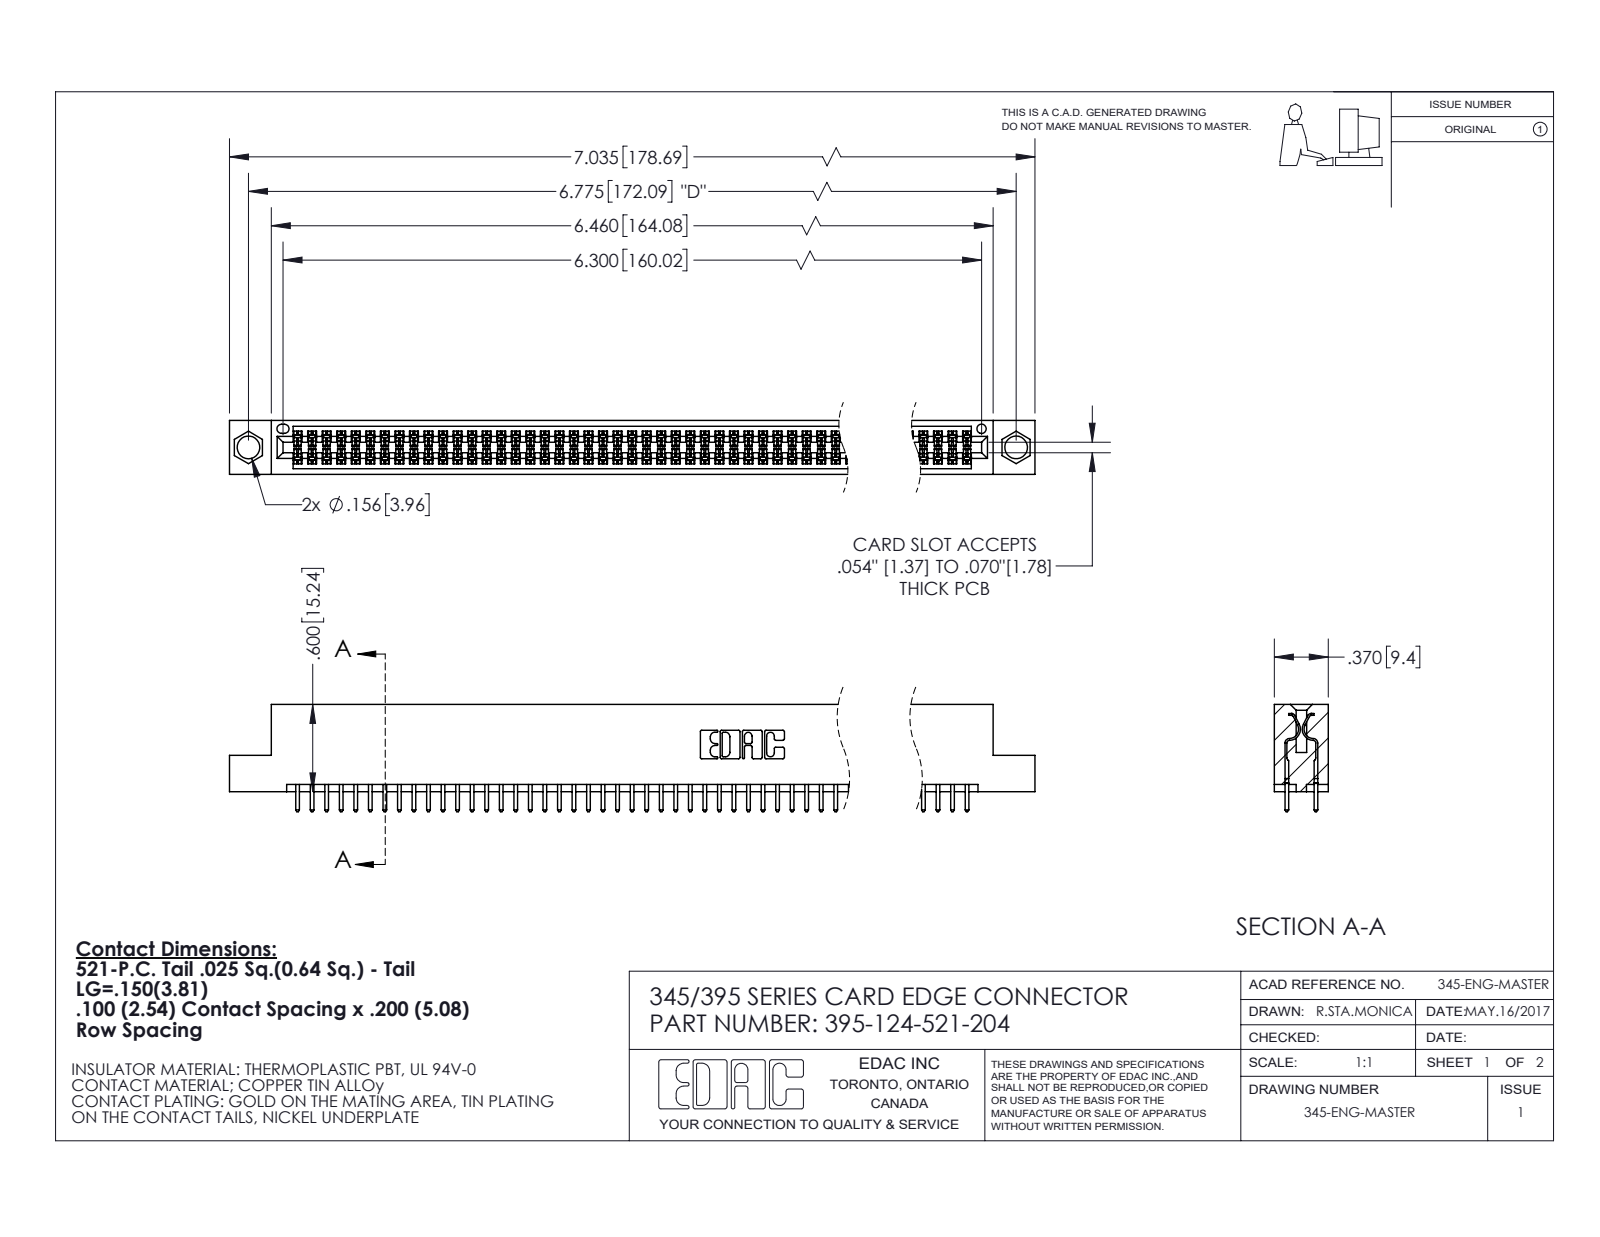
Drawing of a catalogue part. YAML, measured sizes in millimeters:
part_name: "345 Part_Flush Mounting Lugs - 0.156 Dia-TI; 395-124-521-204; 345-292-001_345-293-121"
step_written_by: "SolidWorks 2020 (CONFIG_CONTROL_DESIGN)"
units: millimeters
bodies: {solids: 125, faces: 6340, planar: 4186, cylindrical: 2154, other: 0}
overall_size: [178.7, 18.7, 9.4]
volume: 17390
surface_area: 25610
round_holes:
  - {diameter: 4, count: 2}
  - {diameter: 1.6, count: 1}
partial_cylinders:
  - {radius: 0.2, count: 247}
  - {radius: 0.3, count: 124}
  - {radius: 0.3, count: 22}
  - {radius: 0.2, count: 6}
  - {radius: 0.8, count: 6}
  - {radius: 0.7, count: 3}
  - {radius: 0.4, count: 2}
  - {radius: 0.5, count: 2}
face_to_face_distances: [1.8, 7.6, 5.1, 2.5, 6.9, 0.6, 9.4, 5.7, 4.4, 3.8]
hole_center_spacings: [6.9, 166.1, 172.1]
